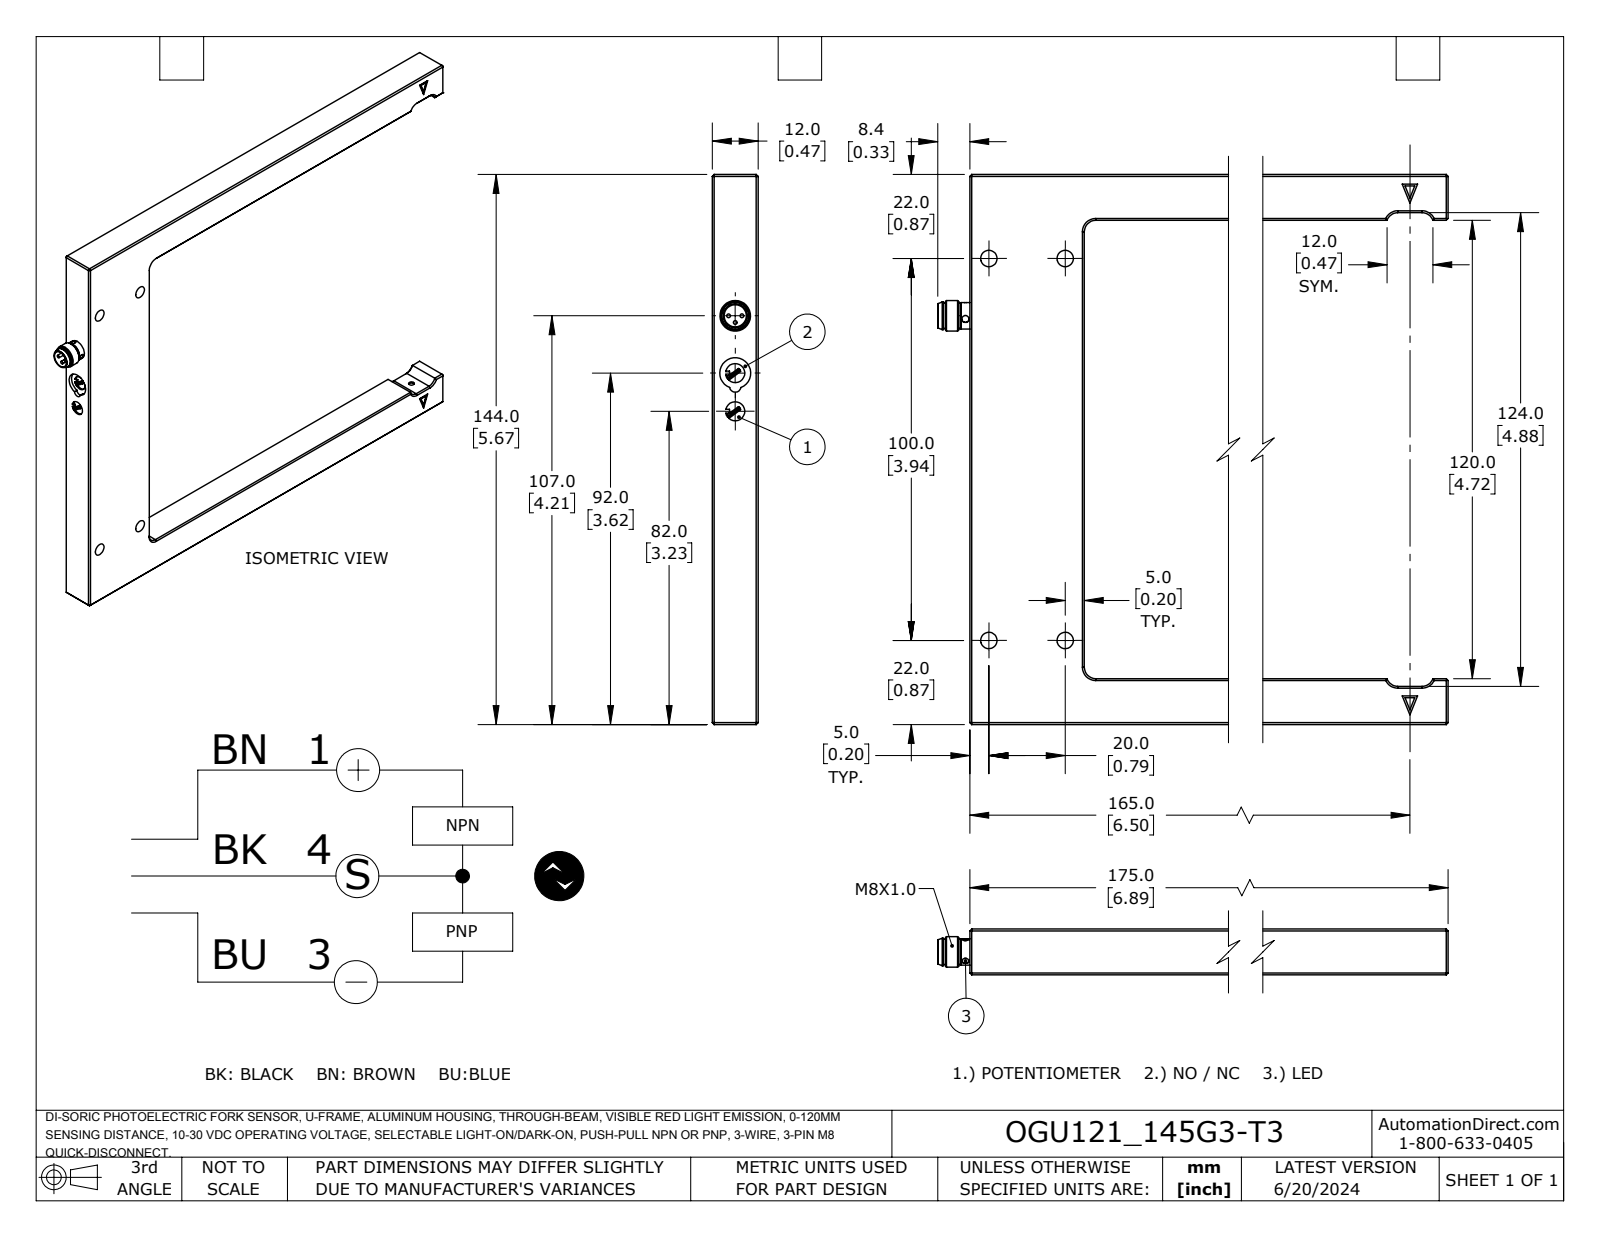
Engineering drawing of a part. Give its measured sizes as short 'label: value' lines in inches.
name: OGU121145G3-T3
written by: SolidWorks 2023 (AUTOMOTIVE_DESIGN)
unit: in
bodies: 1 solid, 159 faces (103 planar, 40 cylindrical, 16 other)
size: 7.22 × 5.669 × 0.472
volume: 5.636 in³; area: 41.97 in²
holes: 4× ⌀0.169, 3× ⌀0.075, 2× ⌀0.197, 1× ⌀0.079, 1× ⌀0.228, 1× ⌀0.319
bosses: 3× ⌀0.039, 1× ⌀0.315, 1× ⌀0.283, 1× ⌀0.272, 1× ⌀0.26, 1× ⌀0.252
rounds: 6× R0.118, 3× R0.059
face distances: 0.472, 5.197, 5.669, 4.724, 1.181, 3.674, 0.64, 4.315, 6.89, 5.709
hole spacings: 0.787, 3.937, 4.015, 0.394, 0.591, 0.984
